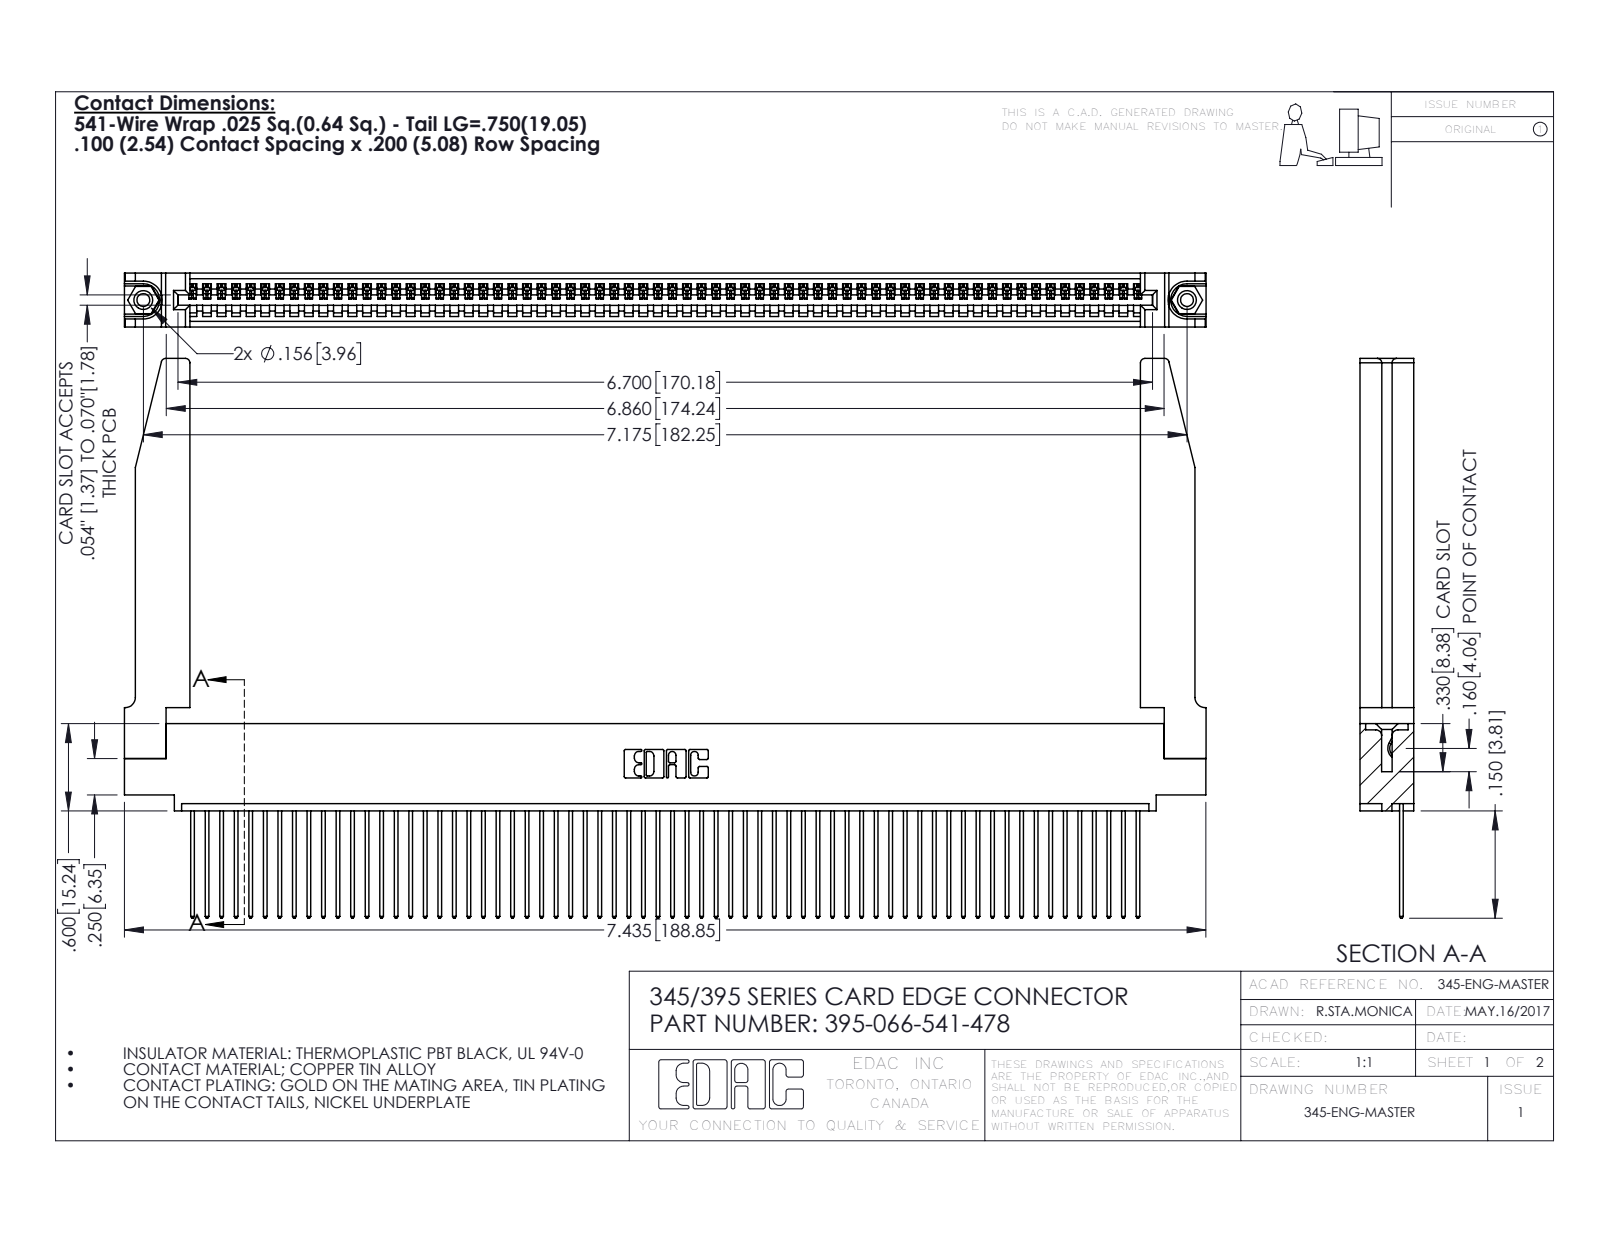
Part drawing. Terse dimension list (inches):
name: 345 Part_0.110 Offset - 0.156 Dia-TH; 395-066-541-478; 345-220-078_345-220-078; 345-292-001_345-293-141 (+1 more)
written by: SolidWorks 2016 (CONFIG_CONTROL_DESIGN)
unit: in
bodies: 71 solids, 4192 faces (2866 planar, 1274 cylindrical, 52 other)
size: 7.436 × 3.847 × 0.37
volume: 1.59 in³; area: 50.88 in²
holes: 2× ⌀0.089, 2× ⌀0.125, 2× ⌀0.156, 1× ⌀0.064
bosses: 2× ⌀0.155
rounds: 132× R0.006, 132× R0.01, 22× R0.01, 8× R0.03, 6× R0.007, 6× R0.031, 3× R0.026, 2× R0.031
face distances: 0.072, 0.298, 0.37, 0.098, 0.272, 0.025, 0.2, 0.225, 0.15, 0.148
hole spacings: 0.27, 6.939, 7.175
